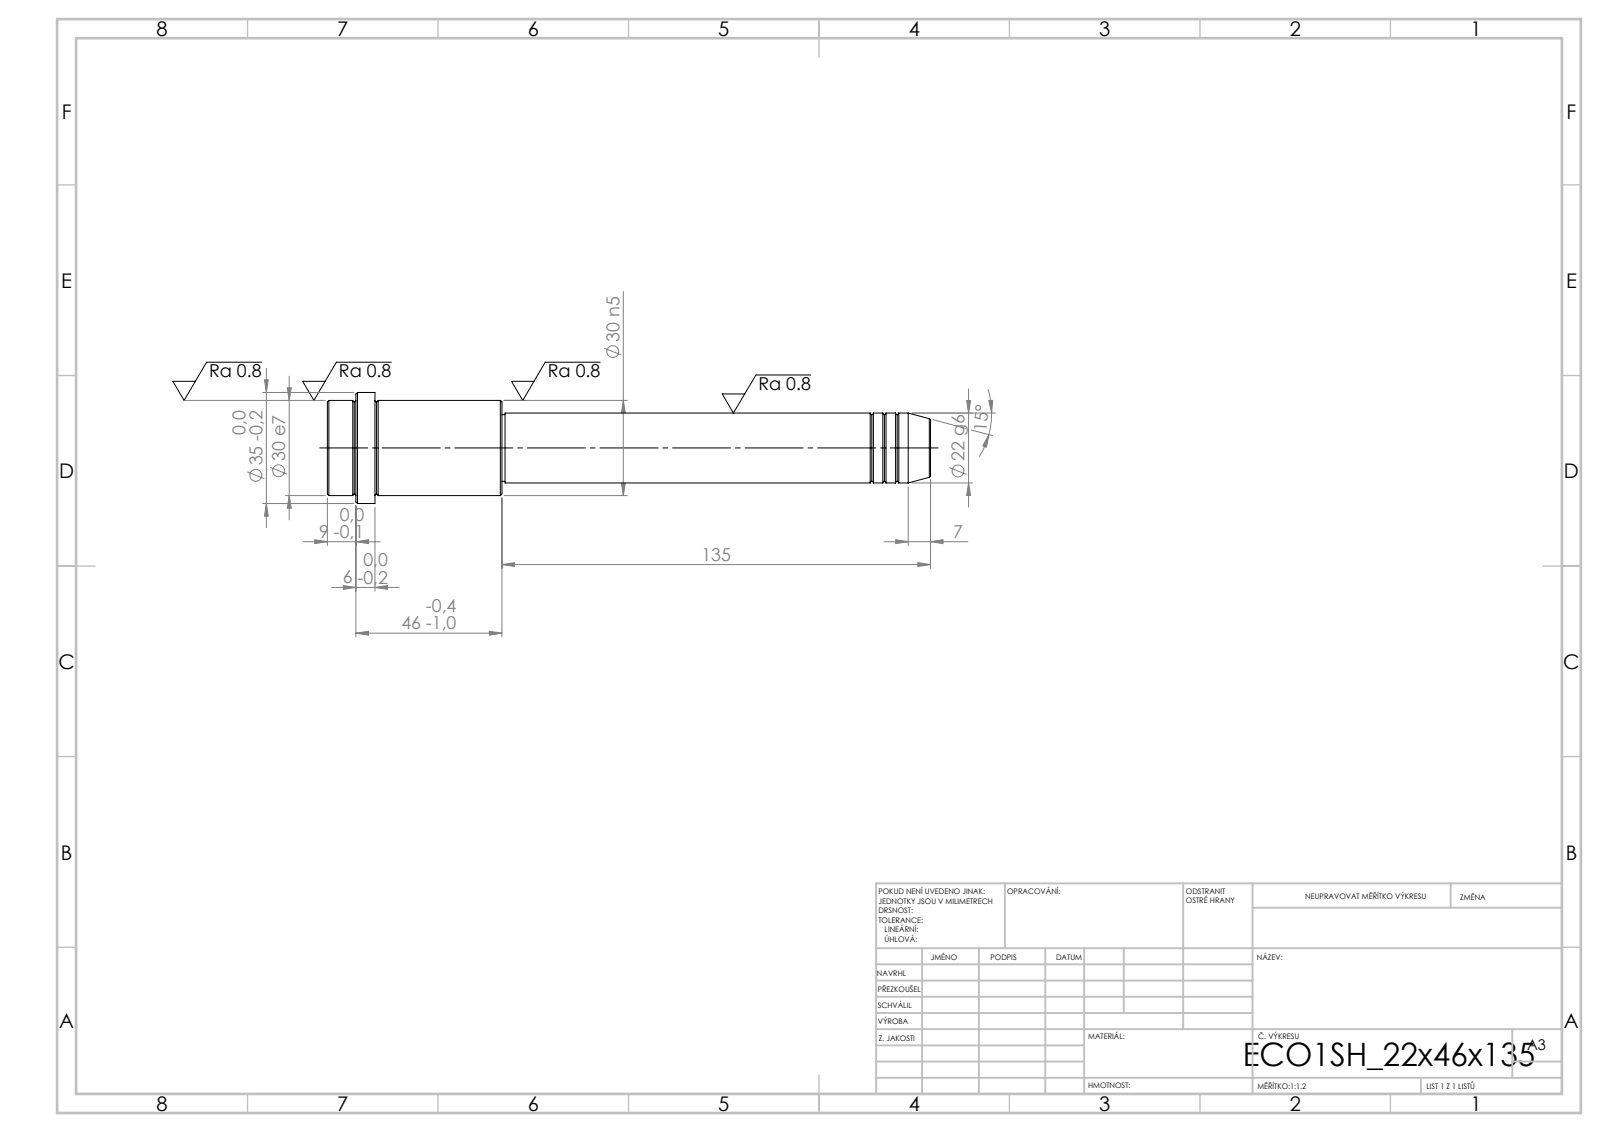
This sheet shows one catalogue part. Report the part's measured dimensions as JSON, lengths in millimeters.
{"step_written_by": "SolidWorks 2019 (CONFIG_CONTROL_DESIGN)", "units": "millimeters", "bodies": {"solids": 1, "faces": 52, "planar": 6, "cylindrical": 16, "other": 30}, "overall_size": [190, 35, 35], "volume_mm3": 91074, "surface_area_mm2": 16568, "round_bosses_or_shafts": [[35, 1], [30, 1], [22, 1], [21, 1]], "face_to_face_distances": [55, 40, 15, 135, 175, 190, 181, 46, 6, 9]}
